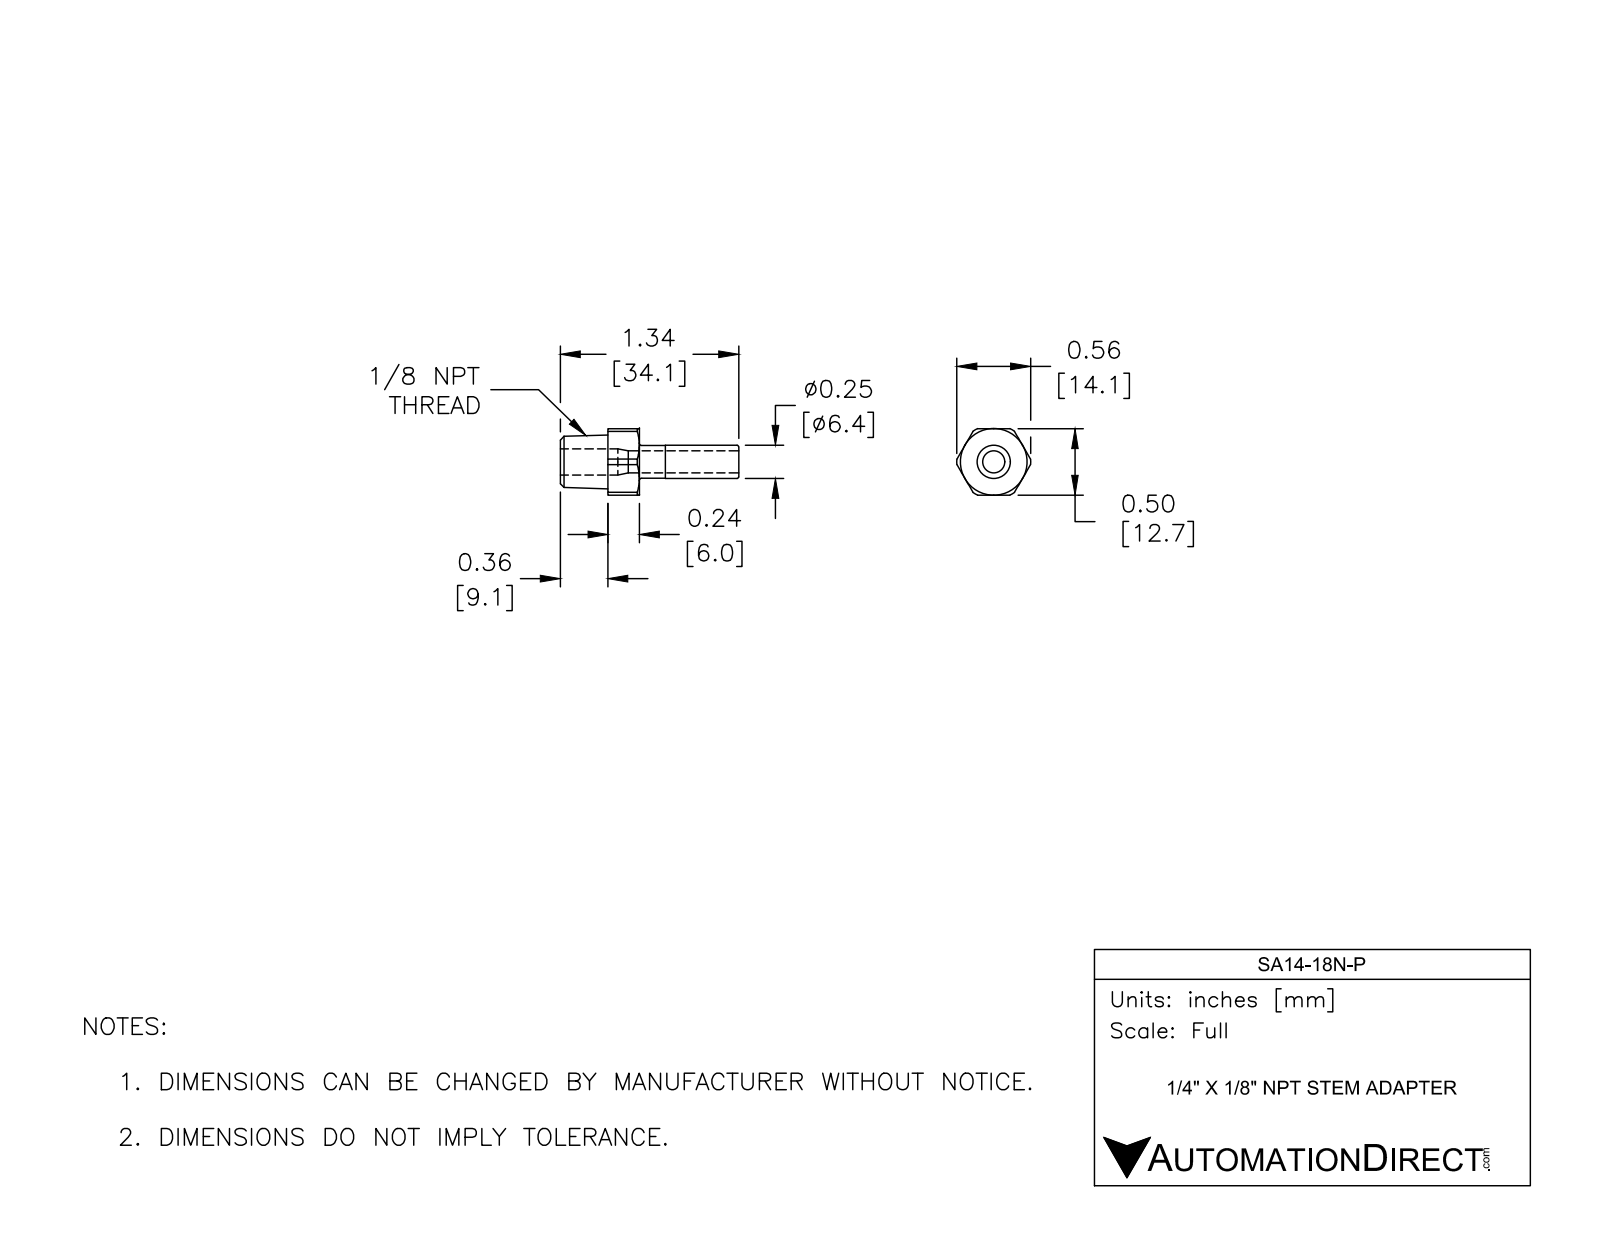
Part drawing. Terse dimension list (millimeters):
name: SA14-18N-P
written by: SolidWorks 2017 (AUTOMOTIVE_DESIGN)
unit: mm
bodies: 1 solid, 43 faces (11 planar, 15 cylindrical, 17 other)
size: 34.1 × 14.1 × 12.7
volume: 1 600 mm³; area: 1 615 mm²
holes: 1× ⌀4.2, 1× ⌀5
bosses: 1× ⌀6.4, 1× ⌀6.2
rounds: 1× R7.1
face distances: 12.7, 6, 9.1, 15.1, 34.1, 25, 19, 20.1, 11, 5
